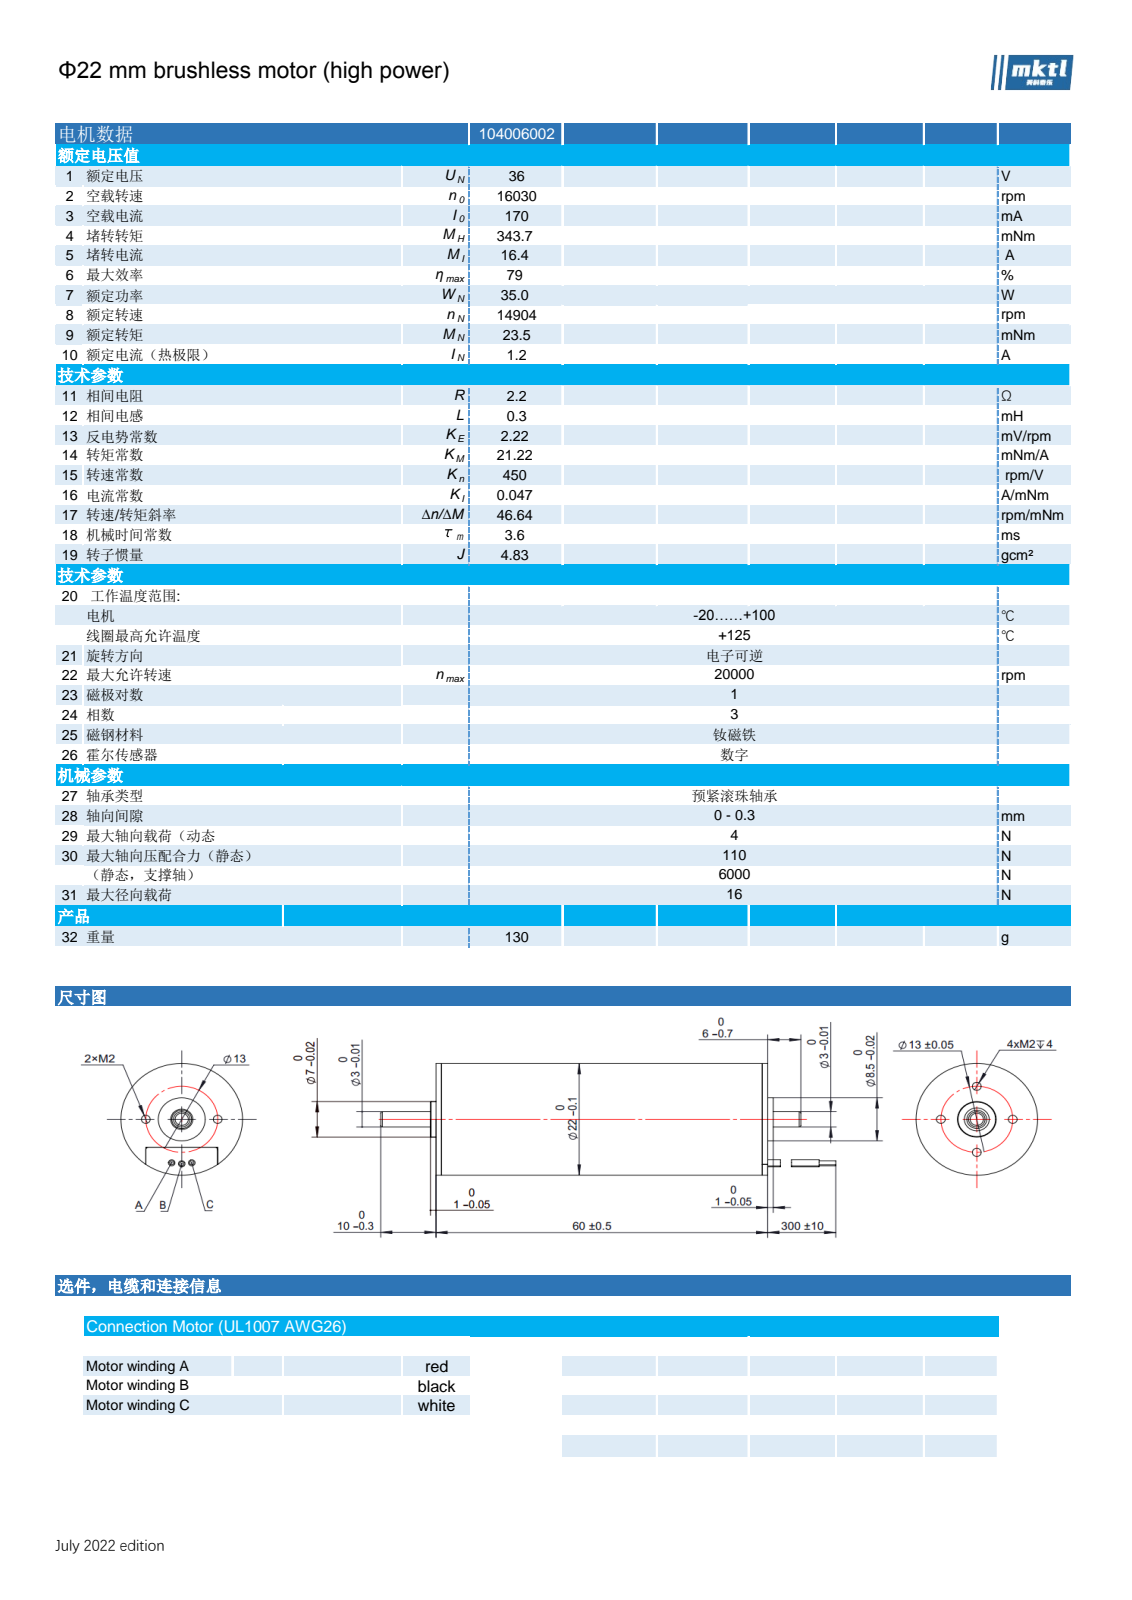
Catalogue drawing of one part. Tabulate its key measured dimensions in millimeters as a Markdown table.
| quantity | value |
| --- | --- |
| part name | 104006002 |
| STEP written by | SolidWorks 2025 (AUTOMOTIVE_DESIGN) |
| units | millimeters |
| bodies | 263 solids, 1850 faces (599 planar, 1200 cylindrical, 51 other) |
| overall size | 83.8 × 22 × 22 |
| volume | 18 884 mm³ |
| surface area | 85 358 mm² |
| round holes (diameter × count) | 0.5 × 4, 1.6 × 4, 0.8 × 3, 3 × 1, 4.5 × 1, 5 × 1, 8 × 1, 11.2 × 1, 11.4 × 1, 14.3 × 1, 14.45 × 1, 16.5 × 1 |
| round bosses / shafts (diameter × count) | 1.2 × 3, 0.3 × 3, 22 × 1, 20.9 × 1, 20.8 × 1, 14.4 × 1, 10.8 × 1, 10.7 × 1 |
| partial cylindrical surfaces (radius × count) | 0.75 × 12, 0.5 × 4, 7.5 × 1, 7.75 × 1, 7.75 × 1, 7.95 × 1, 8.75 × 1, 8.75 × 1 |
| main face-to-face distances | 3, 1.8, 0.4, 2, 38, 36, 1.2, 1, 40.8, 0.8 |
| hole center spacings | 6.5, 8.25, 9.19, 8.75, 1.83, 2.75, 9.76, 10.9 |
